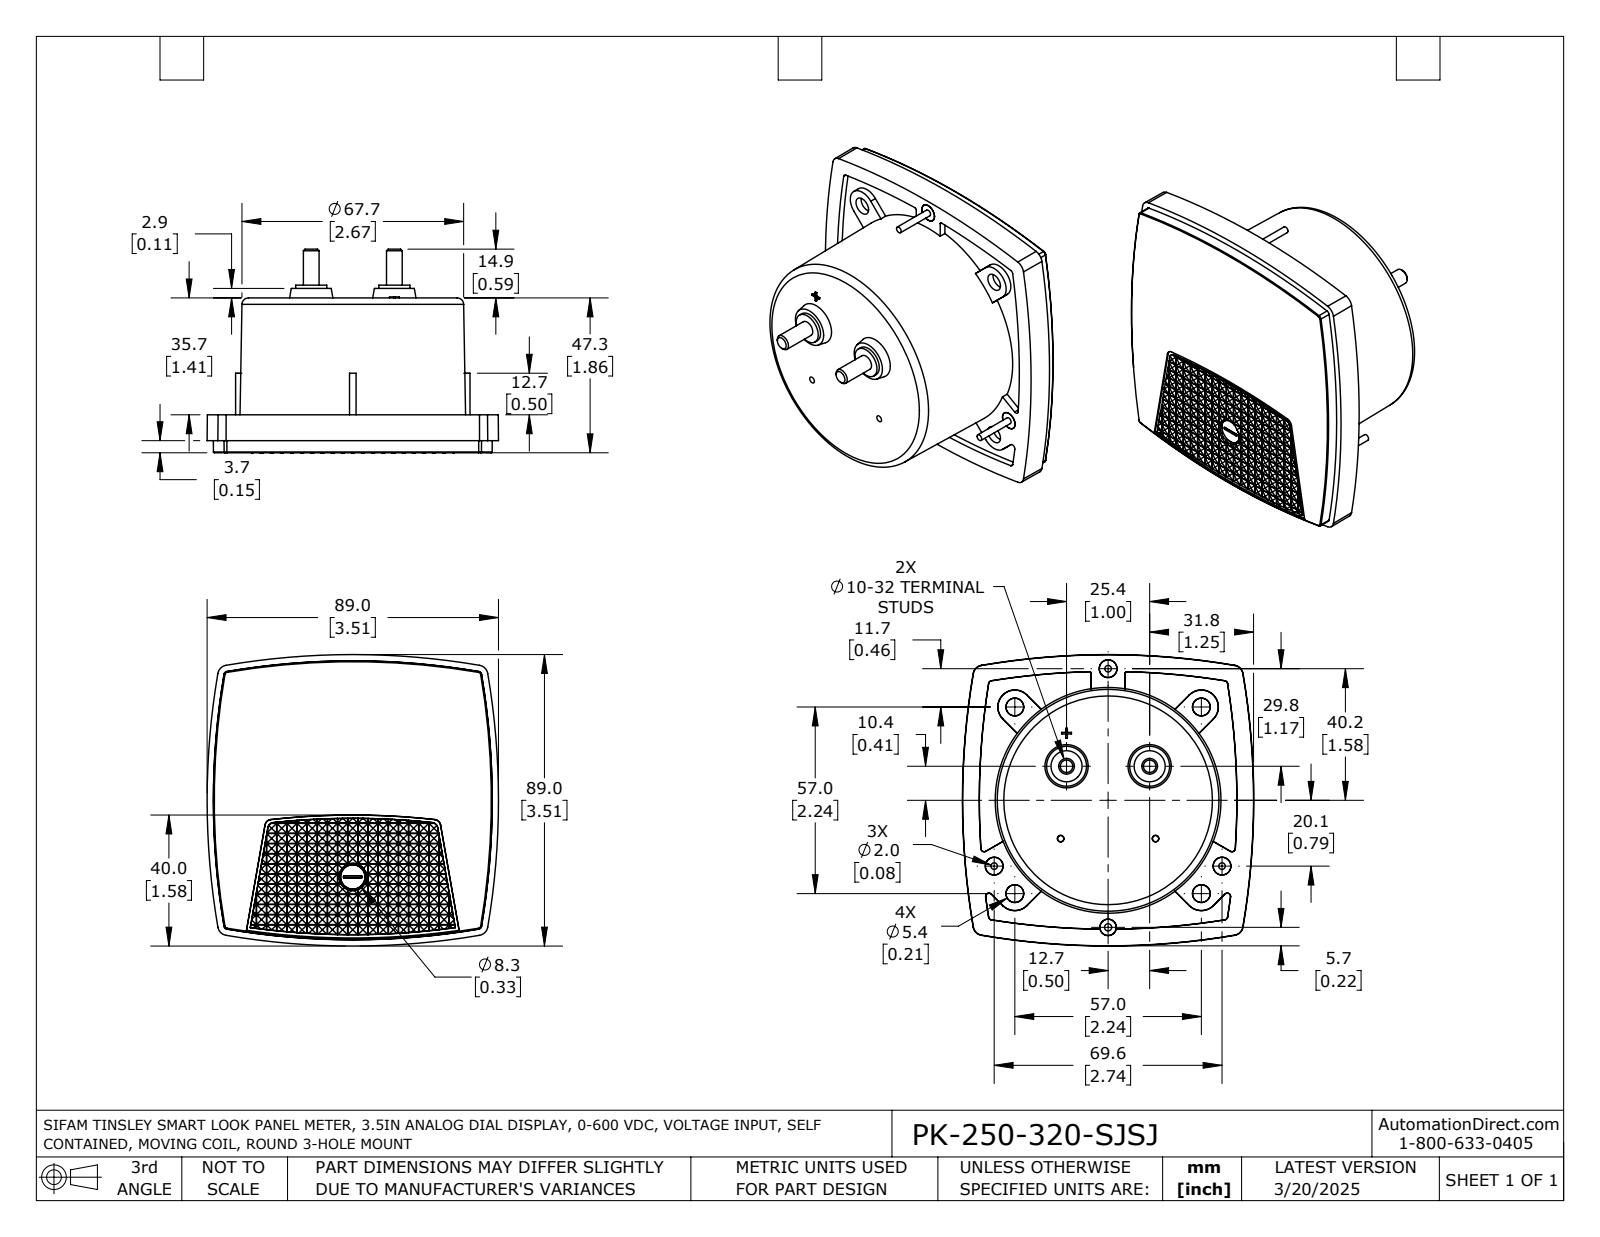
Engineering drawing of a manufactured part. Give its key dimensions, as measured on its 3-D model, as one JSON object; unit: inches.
{"part_name": "PK-250-320-SJSJ", "step_written_by": "SolidWorks 2021 (AUTOMOTIVE_DESIGN)", "units": "inches", "bodies": {"solids": 1, "faces": 1078, "planar": 950, "cylindrical": 23, "other": 105}, "overall_size": [3.505, 3.505, 2.453], "volume_in3": 12.99, "surface_area_in2": 44.29, "round_holes": [[0.087, 1]], "round_bosses_or_shafts": [[0.213, 3], [0.079, 3], [0.374, 2], [0.189, 2]], "partial_cylinders_radius": [[8.961, 1]], "face_to_face_distances": [1.862, 1.406, 0.457, 0.079, 1.484, 0.378, 0.024, 0.096, 0.072, 0.12]}
